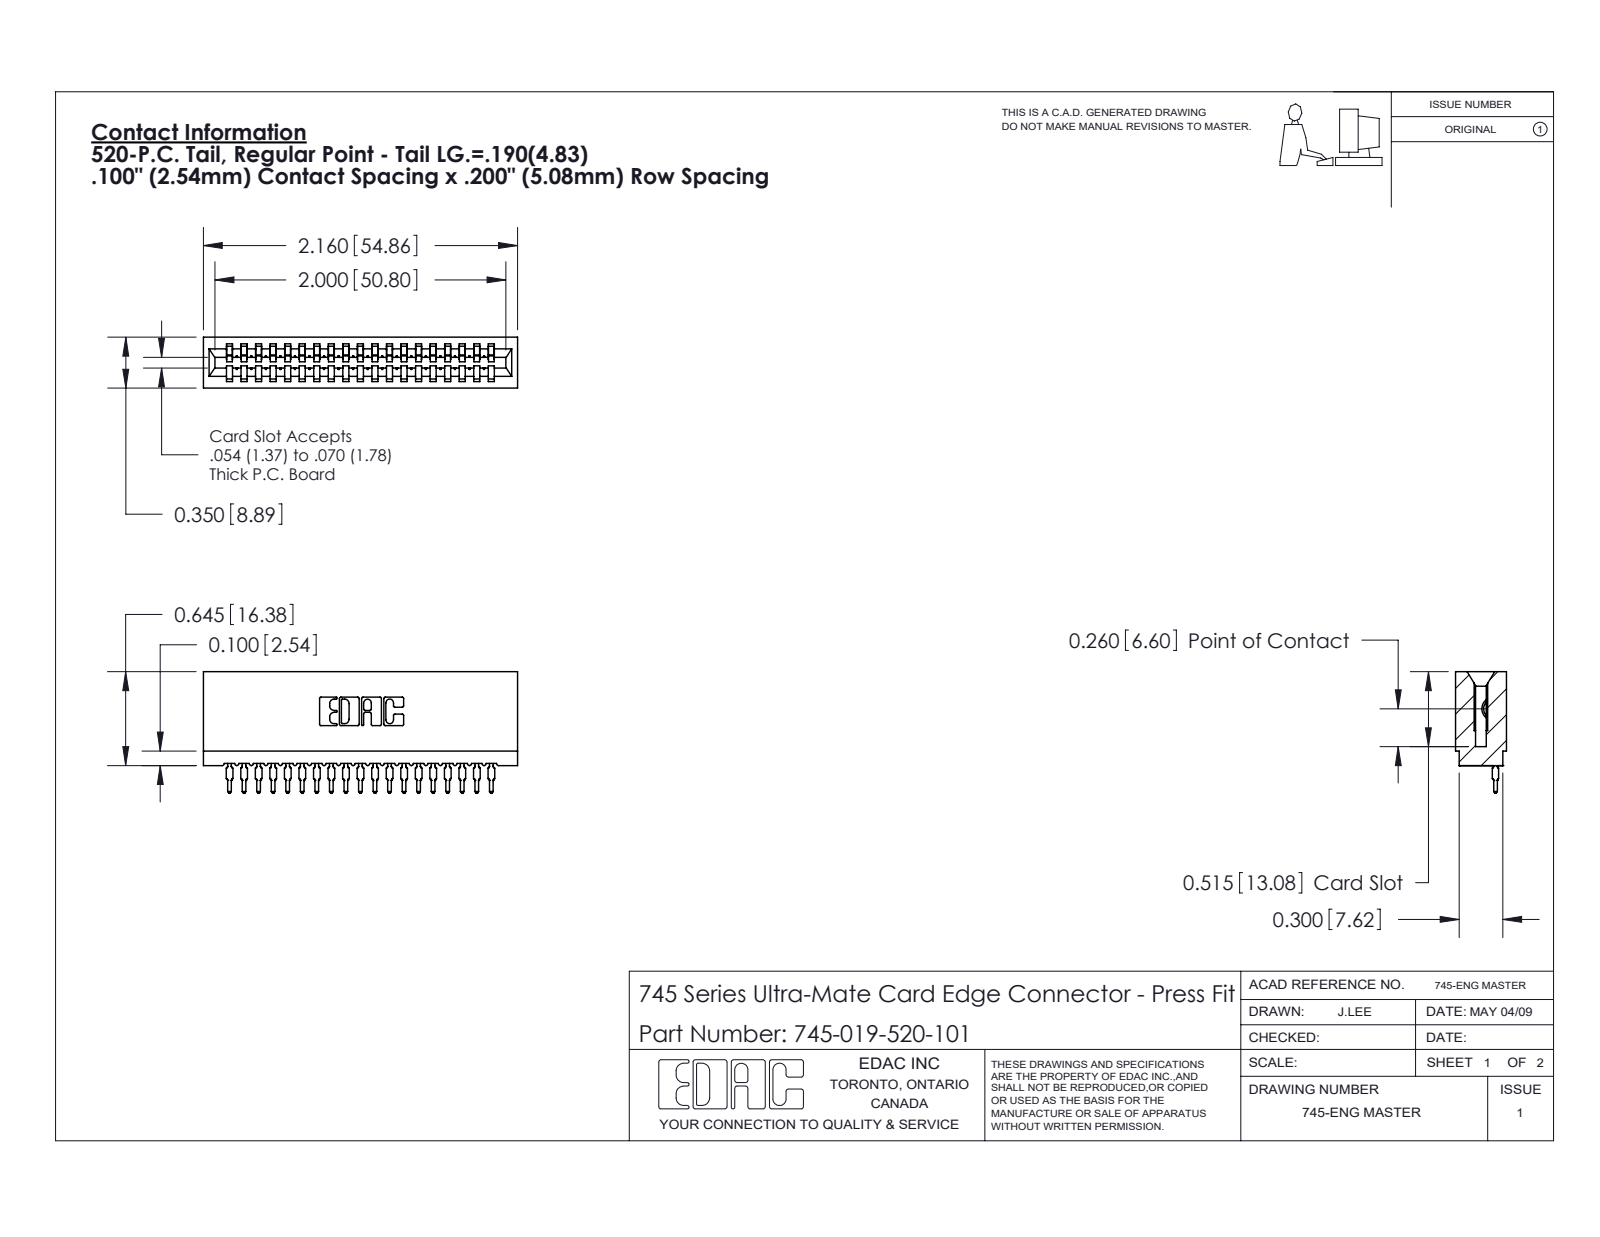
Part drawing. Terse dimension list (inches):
name: 745-292-001_520; 745 Part_Insulator Option - 01; 745-019-520-101
written by: SolidWorks 2020 (CONFIG_CONTROL_DESIGN)
unit: in
bodies: 20 solids, 2223 faces (1328 planar, 401 cylindrical, 494 other)
size: 2.16 × 0.836 × 0.35
volume: 0.298 in³; area: 13.21 in²
rounds: 38× R0.015, 38× R0.021, 22× R0.01, 6× R0.007, 6× R0.031, 4× R0.005, 4× R0.011, 3× R0.026
face distances: 0.1, 0.2, 0.3, 0.4, 0.35, 0.5, 0.6, 0.138, 0.212, 0.7
